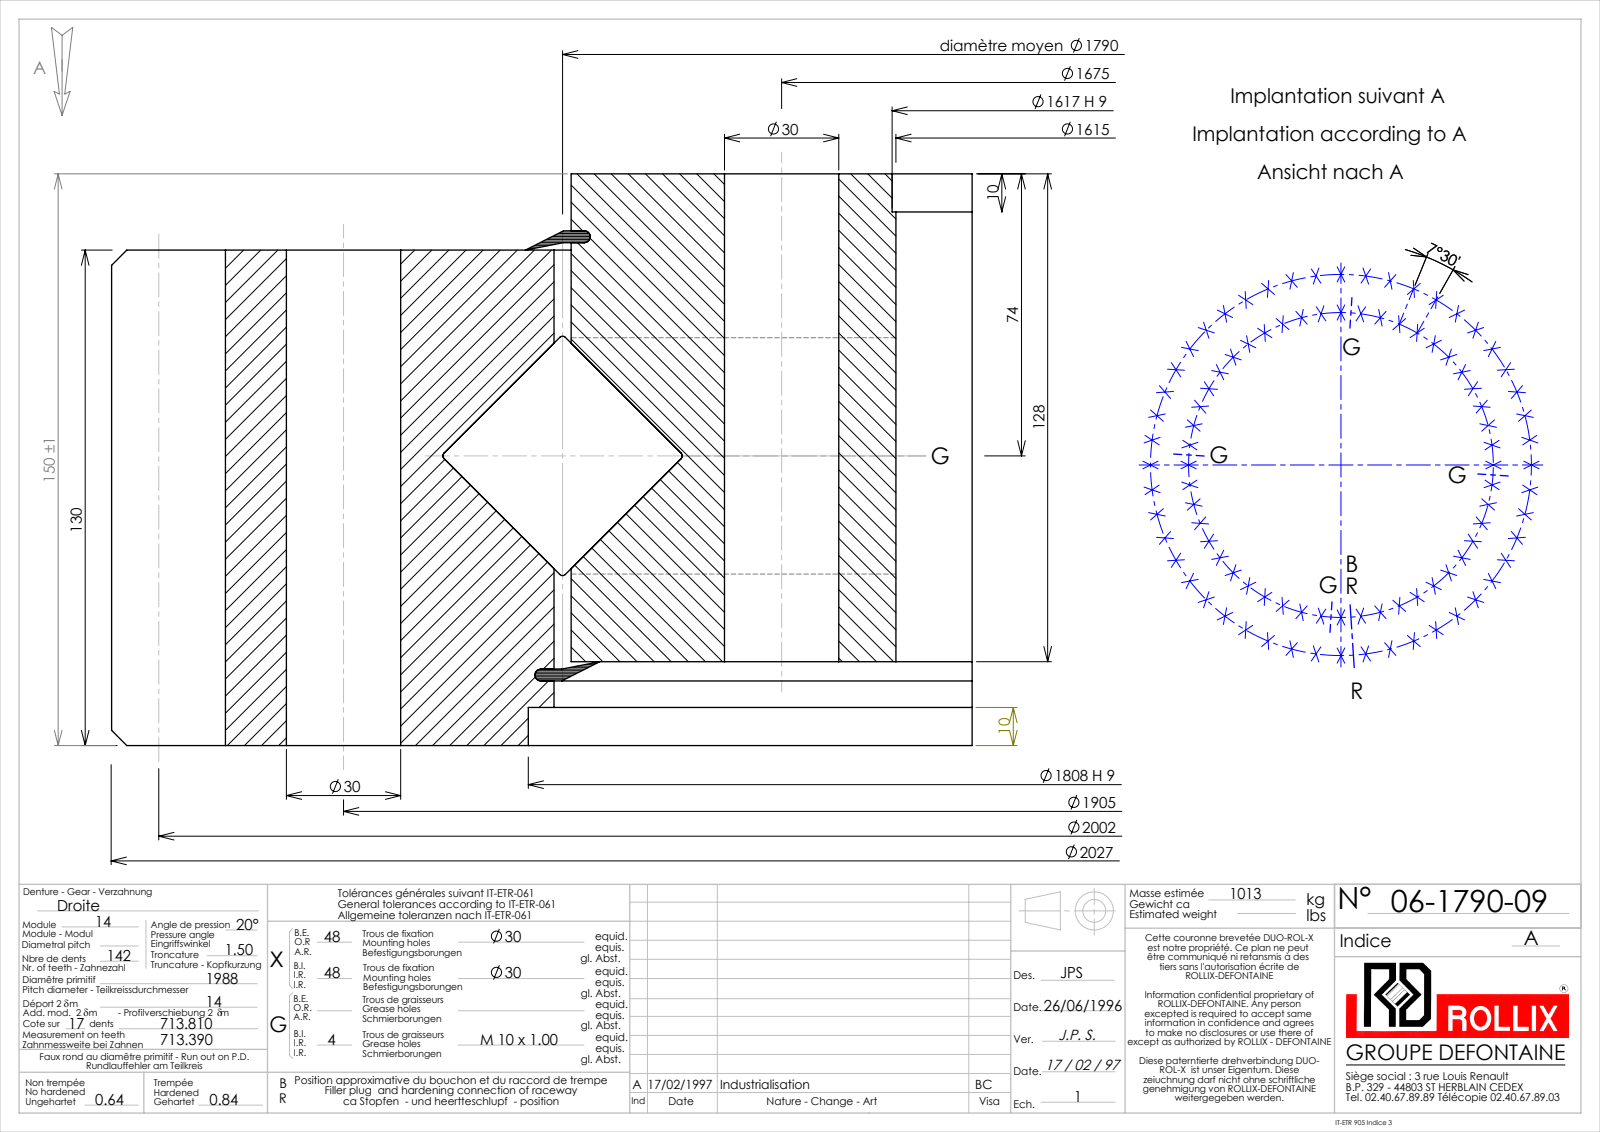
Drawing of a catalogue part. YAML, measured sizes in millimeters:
part_name: "06-1790-09"
step_written_by: "SolidWorks 2016 (CONFIG_CONTROL_DESIGN)"
units: millimeters
bodies: {solids: 5, faces: 1141, planar: 300, cylindrical: 505, other: 336}
overall_size: [2027, 2026.76, 150]
volume: 119000000
surface_area: 7654000
round_holes:
  - {diameter: 30, count: 96}
  - {diameter: 9, count: 4}
  - {diameter: 1615, count: 1}
  - {diameter: 1617, count: 1}
  - {diameter: 1794.5, count: 1}
  - {diameter: 1808, count: 1}
round_bosses_or_shafts:
  - {diameter: 1785.5, count: 1}
  - {diameter: 45, count: 1}
partial_cylinders:
  - {radius: 983.5, count: 1}
  - {radius: 1013.5, count: 1}
face_to_face_distances: [130, 22, 108, 150, 128, 20, 5.05, 113.05, 1.95, 109.95]
hole_center_spacings: [248.65, 124.59, 952.5, 493.05, 842.56, 371.65, 729.01, 1583.95]
